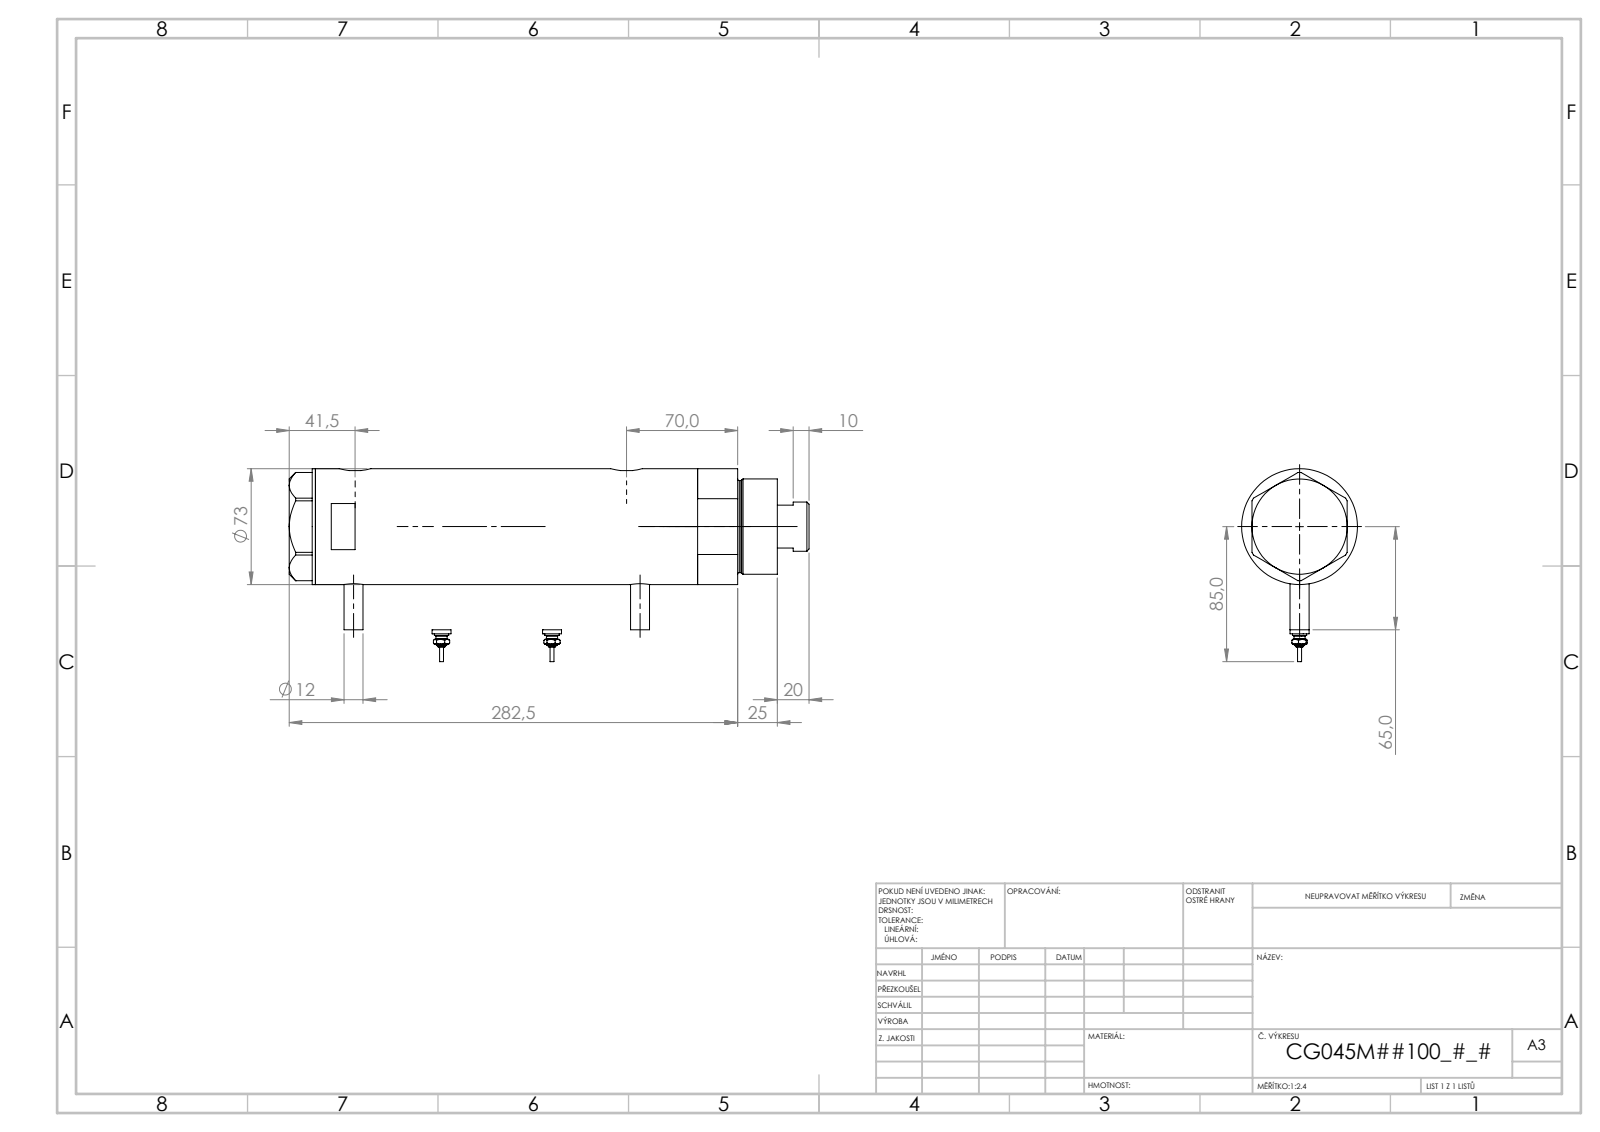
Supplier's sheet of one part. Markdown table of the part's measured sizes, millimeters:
| quantity | value |
| --- | --- |
| part name | V270CG_BACK; V270CG_MIDDLE; V270CG_FRONT; V270CG_SWITCH (+1 more) |
| STEP written by | SolidWorks 2019 (CONFIG_CONTROL_DESIGN) |
| units | millimeters |
| bodies | 6 solids, 231 faces (78 planar, 79 cylindrical, 74 other) |
| overall size | 291.52 × 105.3 × 73 |
| volume | 1 010 000 mm³ |
| surface area | 169 011 mm² |
| round holes (diameter × count) | 5 × 2, 12.5 × 2, 13.16 × 2, 10.5 × 1, 32 × 1, 33.5 × 1, 45 × 1, 48 × 1, 64 × 1 |
| round bosses / shafts (diameter × count) | 12 × 3, 9 × 2, 7 × 2, 4.34 × 2, 2.4 × 2, 73 × 1, 60 × 1, 58 × 1 |
| partial cylindrical surfaces (radius × count) | 10 × 2 |
| main face-to-face distances | 141.15, 42.5, 183.65, 16.5, 16.51, 26, 167.15, 25.99, 167.14, 255.02 |
| hole center spacings | 151.65, 0.99, 1, 8.5, 8.51, 142.15, 143.14, 143.15 |
